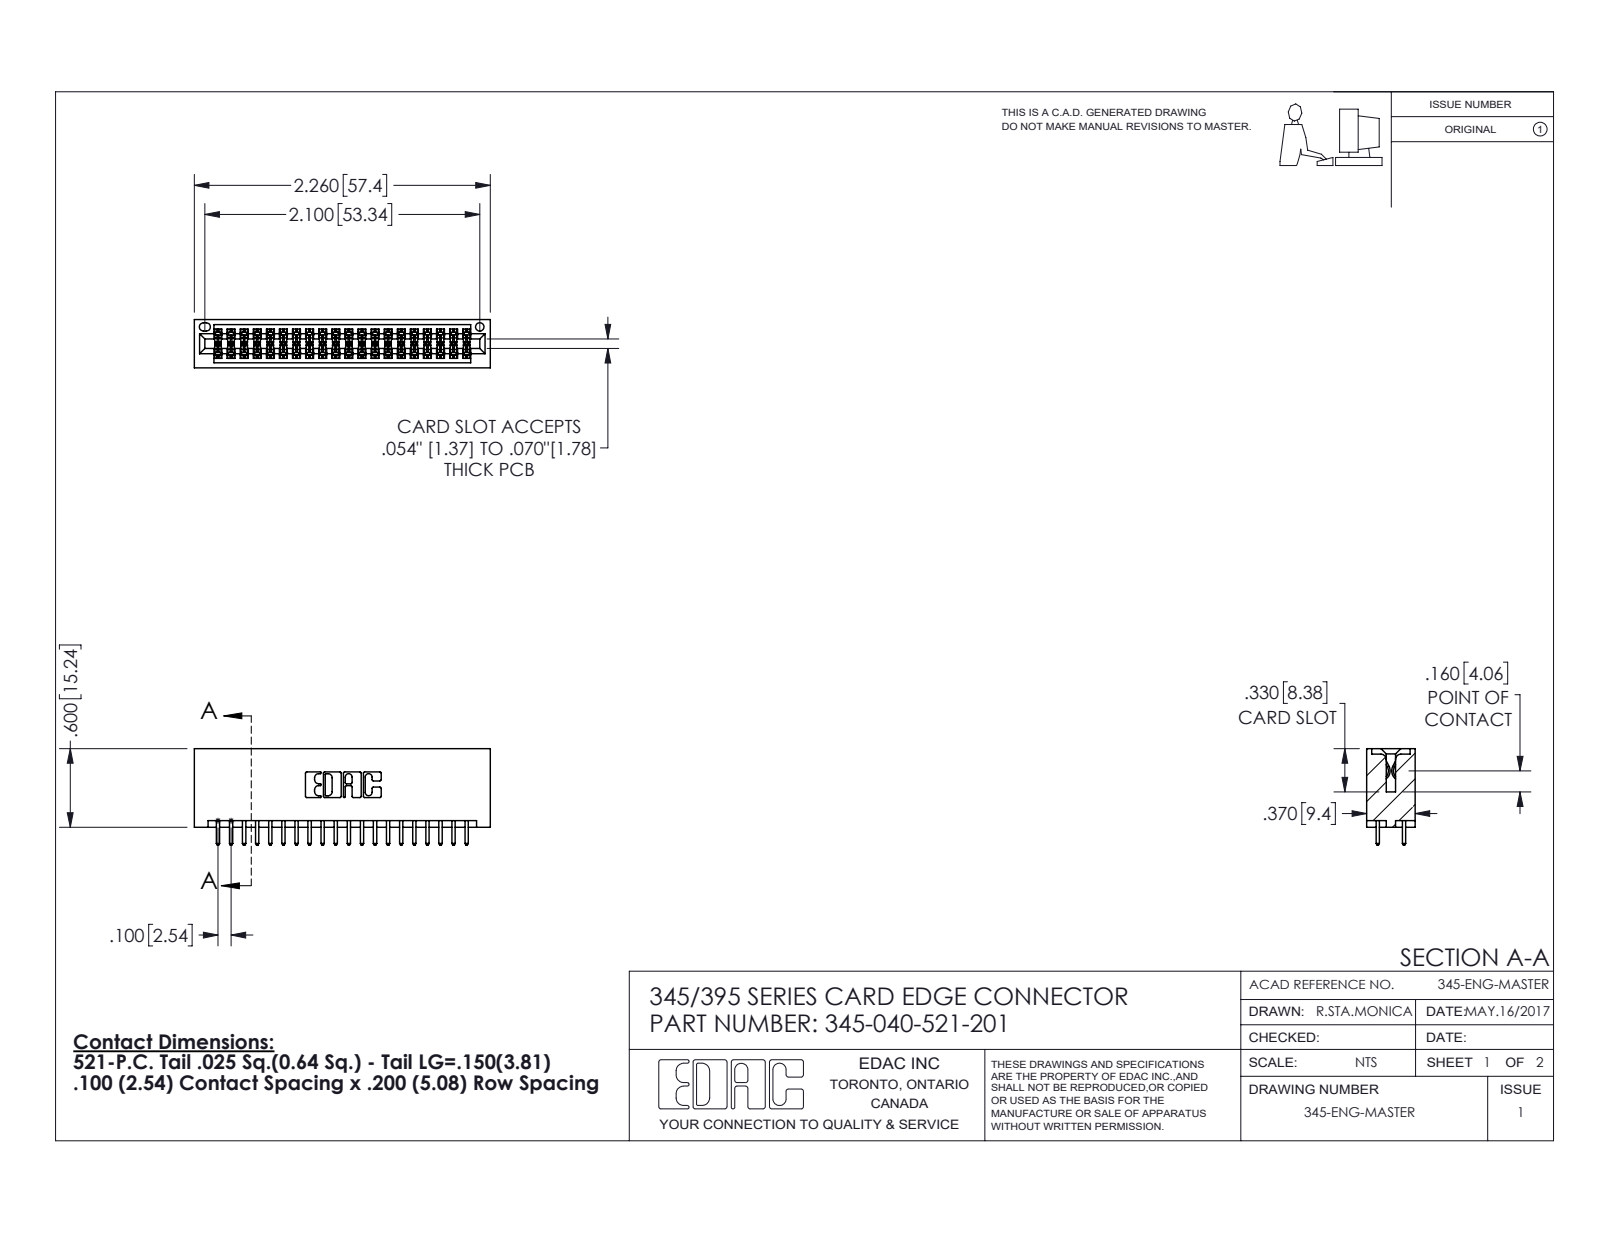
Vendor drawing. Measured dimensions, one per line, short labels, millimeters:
name: 345 Part_No Mounting Lugs; 345-040-521-201; 345-292-001_345-293-121
written by: SolidWorks 2016 (CONFIG_CONTROL_DESIGN)
unit: mm
bodies: 41 solids, 2118 faces (1396 planar, 722 cylindrical, 0 other)
size: 57.4 × 18.7 × 9.4
volume: 5 960 mm³; area: 8 600 mm²
holes: 1× ⌀1.6
rounds: 60× R0.2, 40× R0.3, 22× R0.3, 6× R0.2, 6× R0.8, 3× R0.7, 2× R0.4, 2× R0.5
face distances: 7.6, 1.8, 5.1, 9.4, 2.5, 6.9, 0.6, 5.7, 4.4, 2.5
